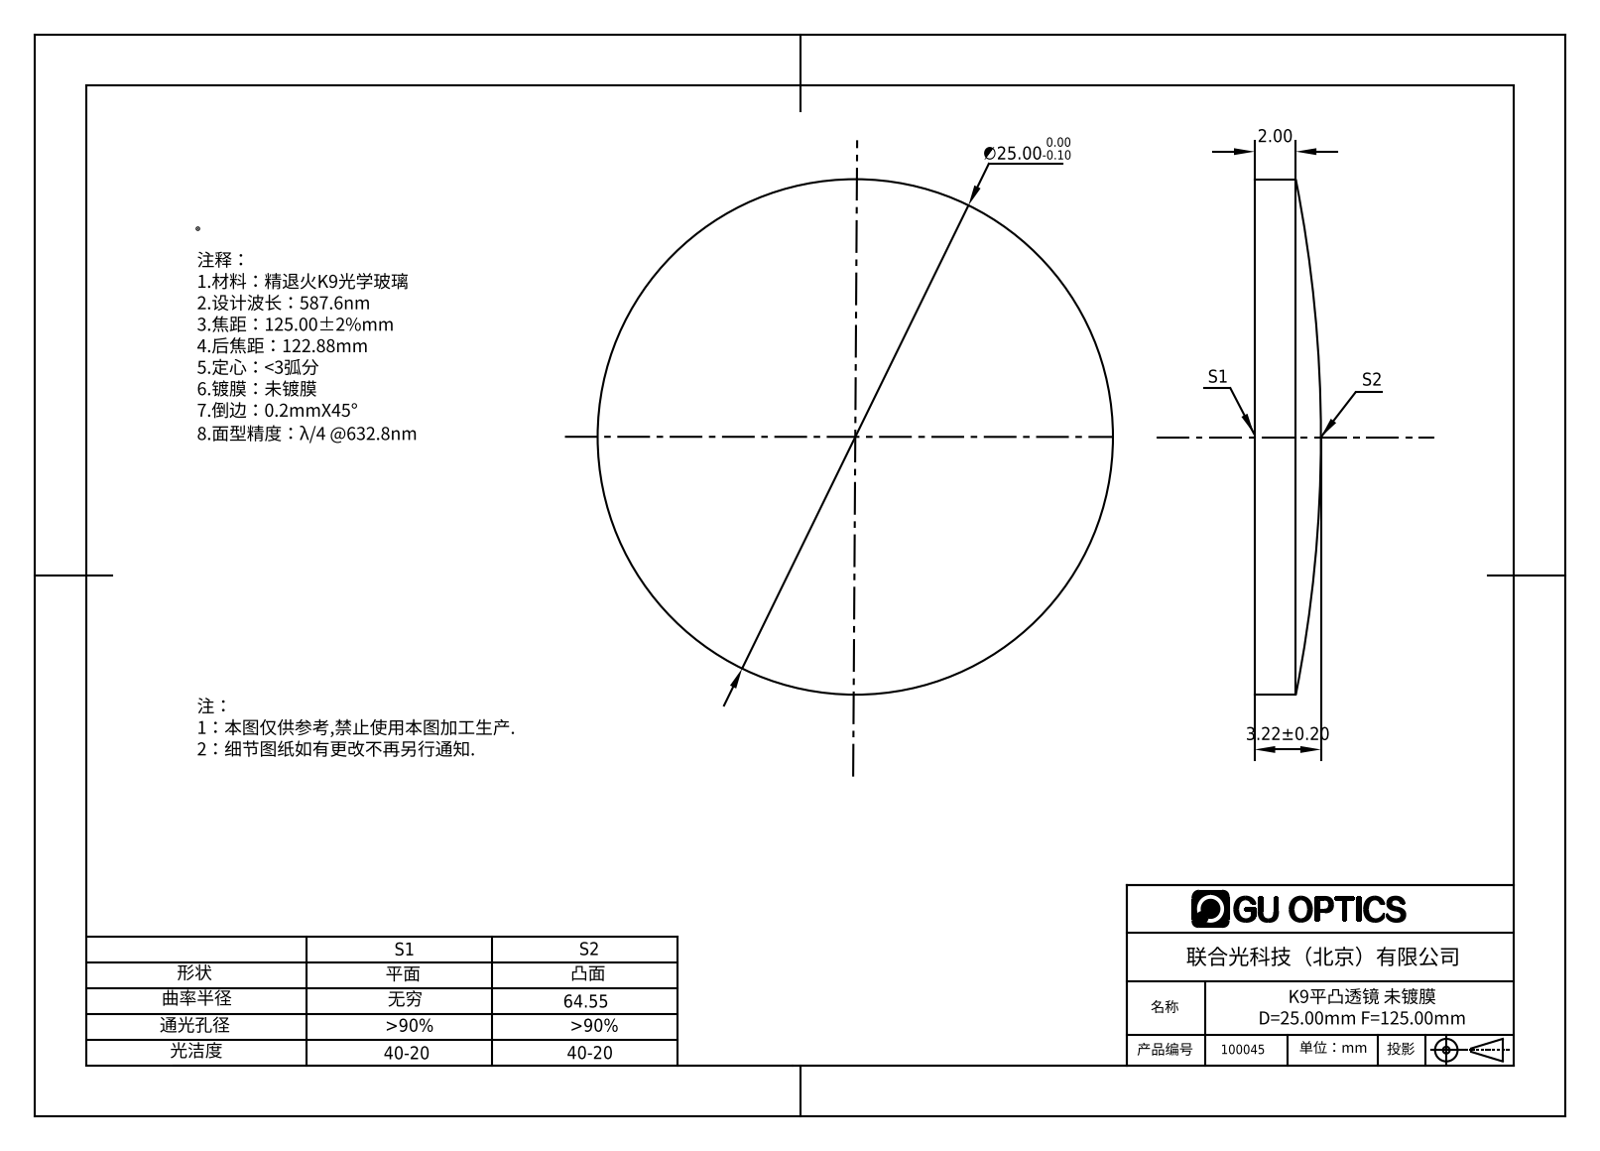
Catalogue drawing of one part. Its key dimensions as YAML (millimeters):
part_name: "100045"
step_written_by: "SolidWorks 2016 (AUTOMOTIVE_DESIGN)"
units: millimeters
bodies: {solids: 1, faces: 5, planar: 1, cylindrical: 2, other: 2}
overall_size: [25, 25, 3.22]
volume: 1282
surface_area: 1144
round_bosses_or_shafts:
  - {diameter: 25, count: 1}
